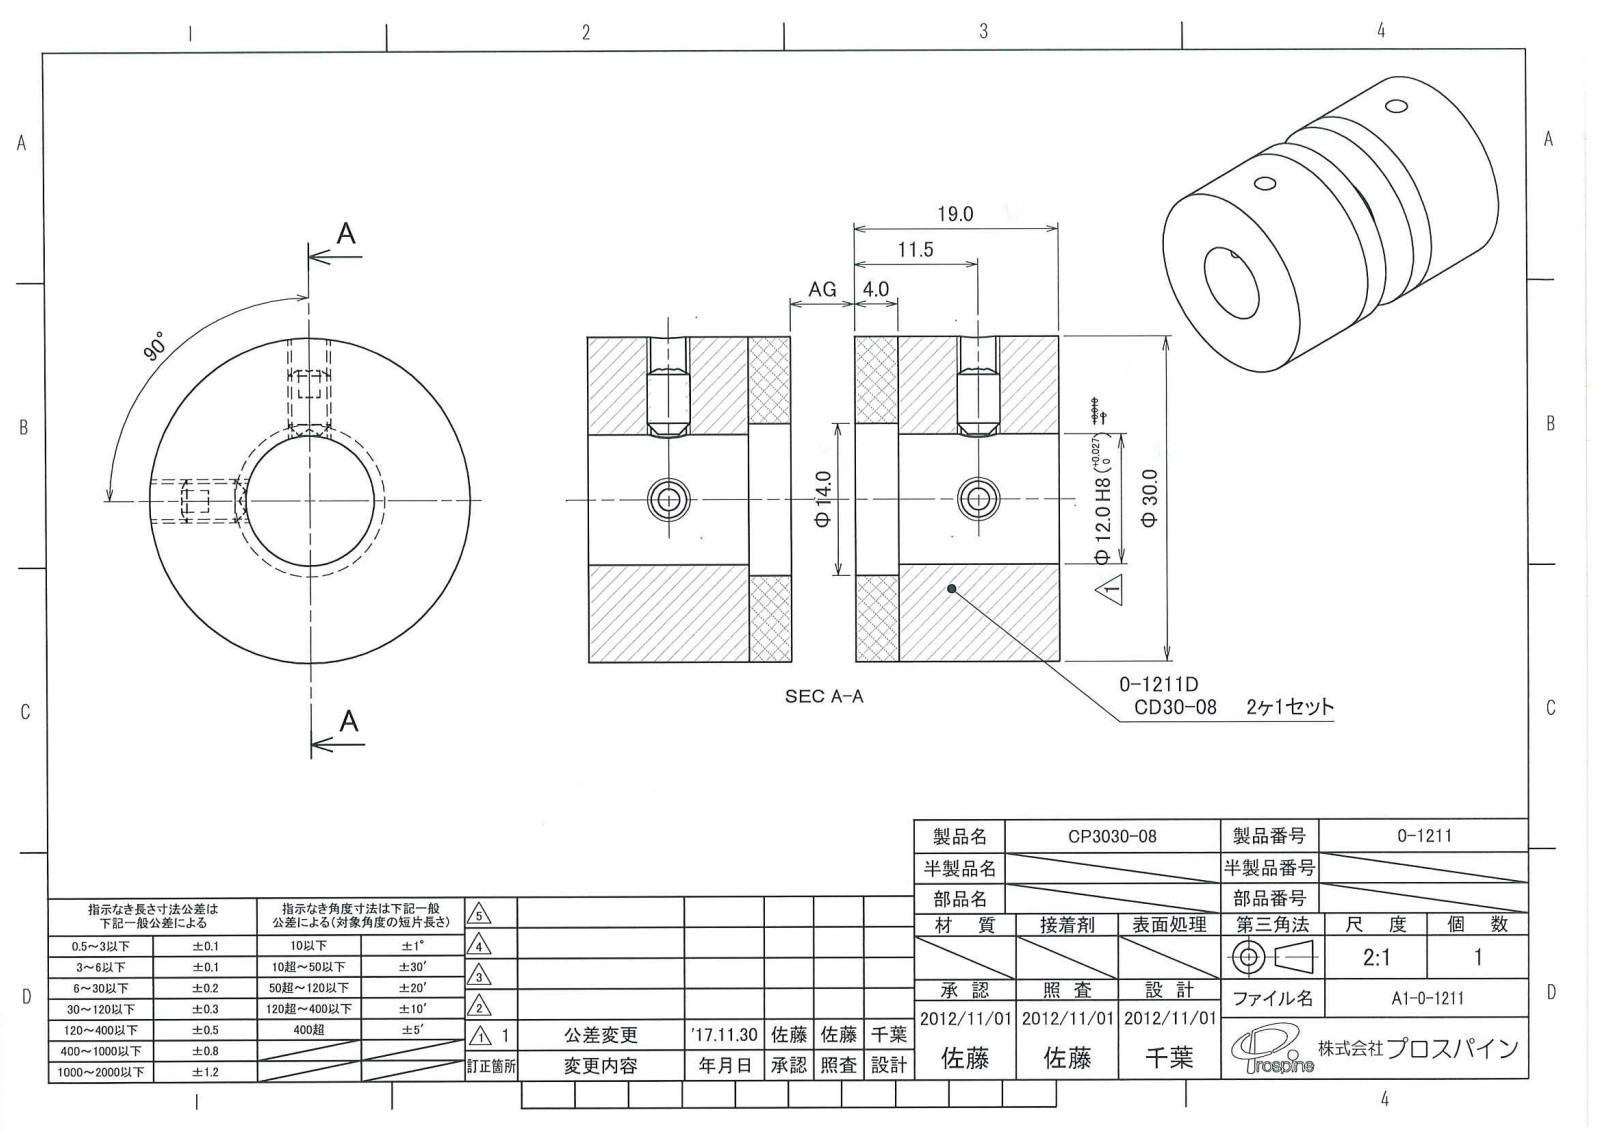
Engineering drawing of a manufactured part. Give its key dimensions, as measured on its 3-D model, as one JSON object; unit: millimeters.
{"step_written_by": "PSStep 10.0 (CONFIG_CONTROL_DESIGN)", "units": "millimeters", "bodies": {"solids": 5, "faces": 43, "planar": 25, "cylindrical": 9, "other": 9}, "overall_size": [300, 30, 21], "volume_mm3": 11138, "surface_area_mm2": 5292, "round_holes": [[3.3, 2], [12, 1], [14, 1]], "round_bosses_or_shafts": [[4, 3], [30, 1]], "face_to_face_distances": [15, 19, 4, 2, 1.99, 8.5, 10.5, 18.5, 3.5, 0.5]}
